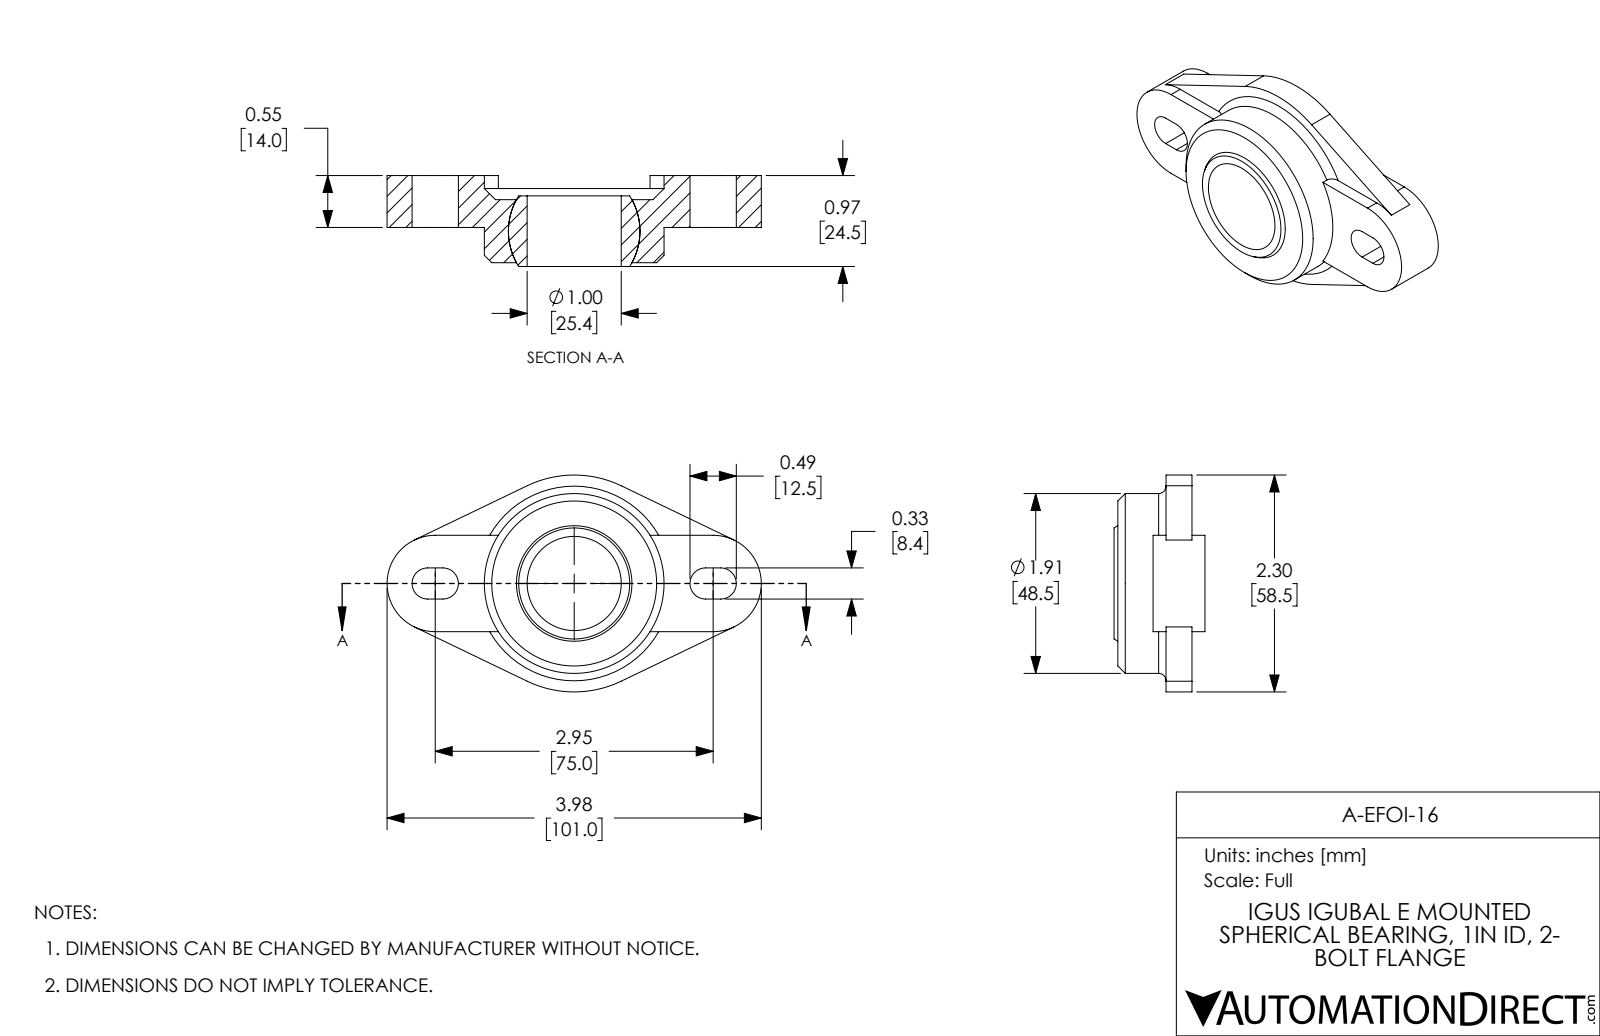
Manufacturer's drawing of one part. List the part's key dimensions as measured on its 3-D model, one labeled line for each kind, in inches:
Part name (STEP PRODUCT): A-EFOI-16
STEP written by: SolidWorks 2017 (AUTOMOTIVE_DESIGN)
Units: inches
Bodies: 2 solids, 56 faces (28 planar, 18 cylindrical, 10 other)
Overall size (bounding box): 3.976 × 2.303 × 1.29
Volume: 2.761 in³ · Surface area: 27.41 in²
Round holes (diameter × count): ⌀1 ×1, ⌀1.909 ×1
Partial cylindrical surfaces — rounded edges, fillets, slot ends (radius × count): R0.165 ×4, R0.512 ×2, R1.152 ×1
Main face-to-face distances: 0.138, 0.413, 0.551, 0.925, 0.787, 0.374, 0.276, 0.512, 0.256, 0.118
